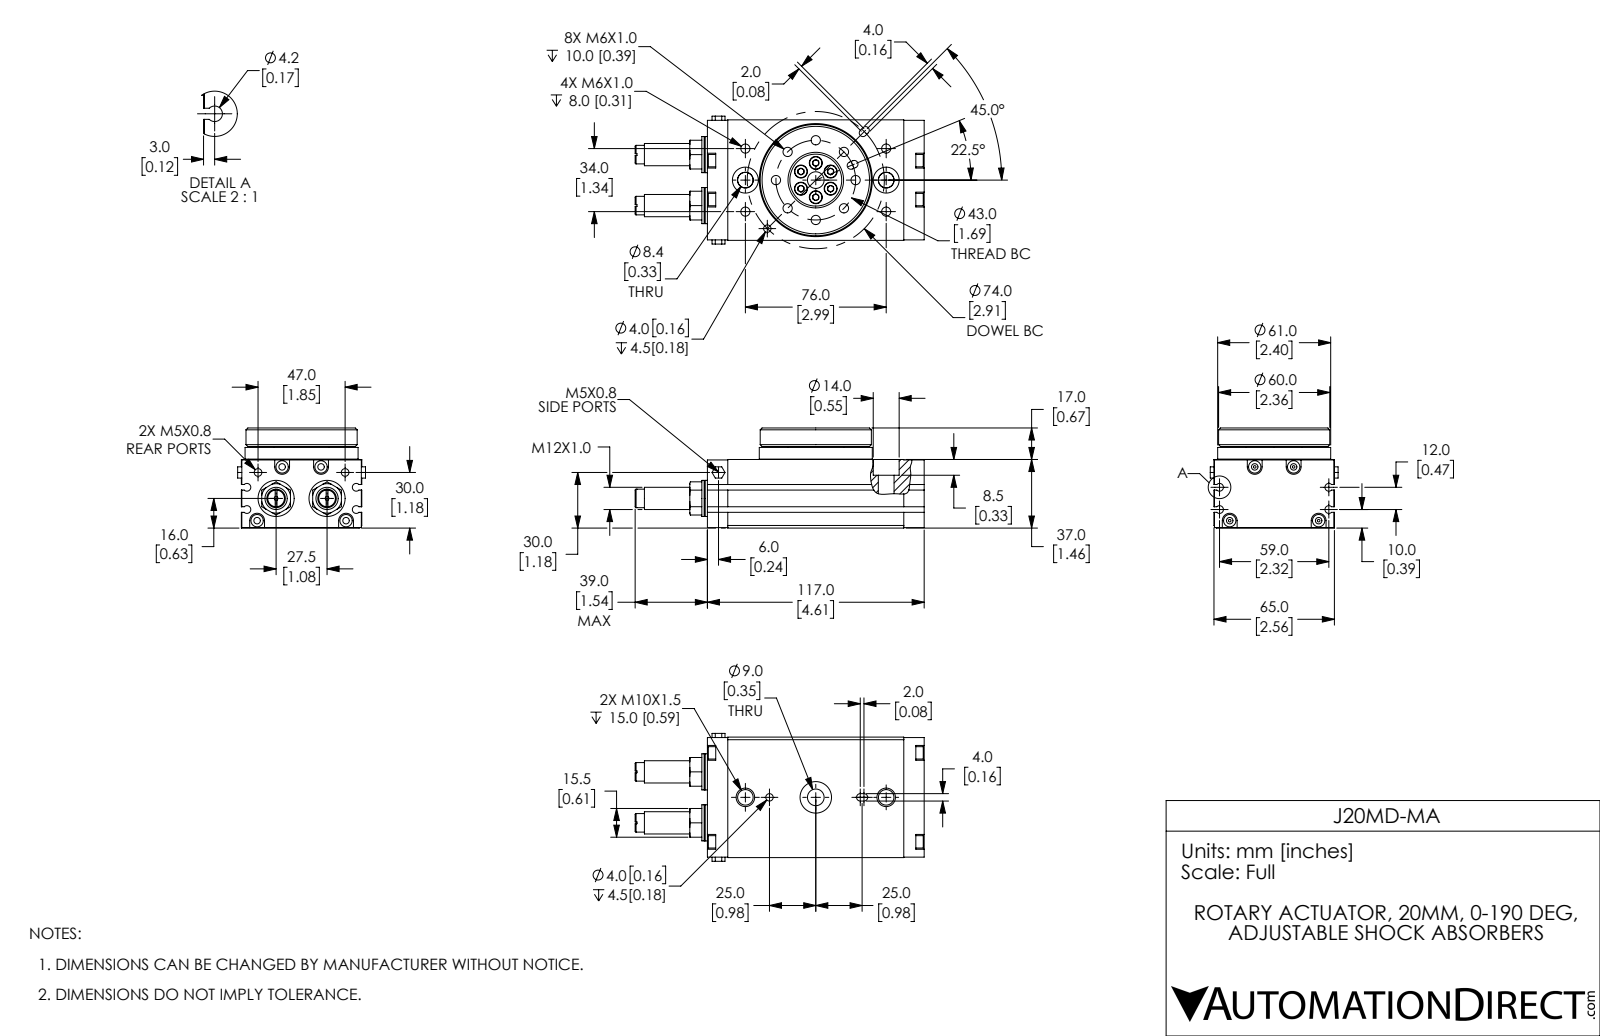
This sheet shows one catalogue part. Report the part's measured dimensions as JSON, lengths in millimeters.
{"part_name": "J20MD-MA_table; J20MD-MA_body2; J20MD-MA; J20MD-MA_M4_91290A138", "step_written_by": "SolidWorks 2017 (AUTOMOTIVE_DESIGN)", "units": "millimeters", "bodies": {"solids": 8, "faces": 709, "planar": 217, "cylindrical": 328, "other": 164}, "overall_size": [156, 69, 54], "volume_mm3": 311088, "surface_area_mm2": 55786, "round_holes": [[5, 8], [3.5, 4], [4.92, 4], [4, 3], [2, 2], [4.13, 2], [8.38, 2], [8.5, 2], [14, 2], [9, 1], [17, 1], [28, 1]], "round_bosses_or_shafts": [[7, 6], [4, 6], [3.09, 6], [6.66, 4], [19.5, 2], [12, 2], [10, 2], [61, 1]], "partial_cylinders_radius": [[2, 6], [2.1, 4], [4, 4]], "face_to_face_distances": [37, 65, 6.5, 0.5, 36.75, 7, 44, 43.5, 17, 10.5], "hole_center_spacings": [16.45, 21.5, 39.72, 9.25, 17, 22.87, 23.69, 27.4]}
